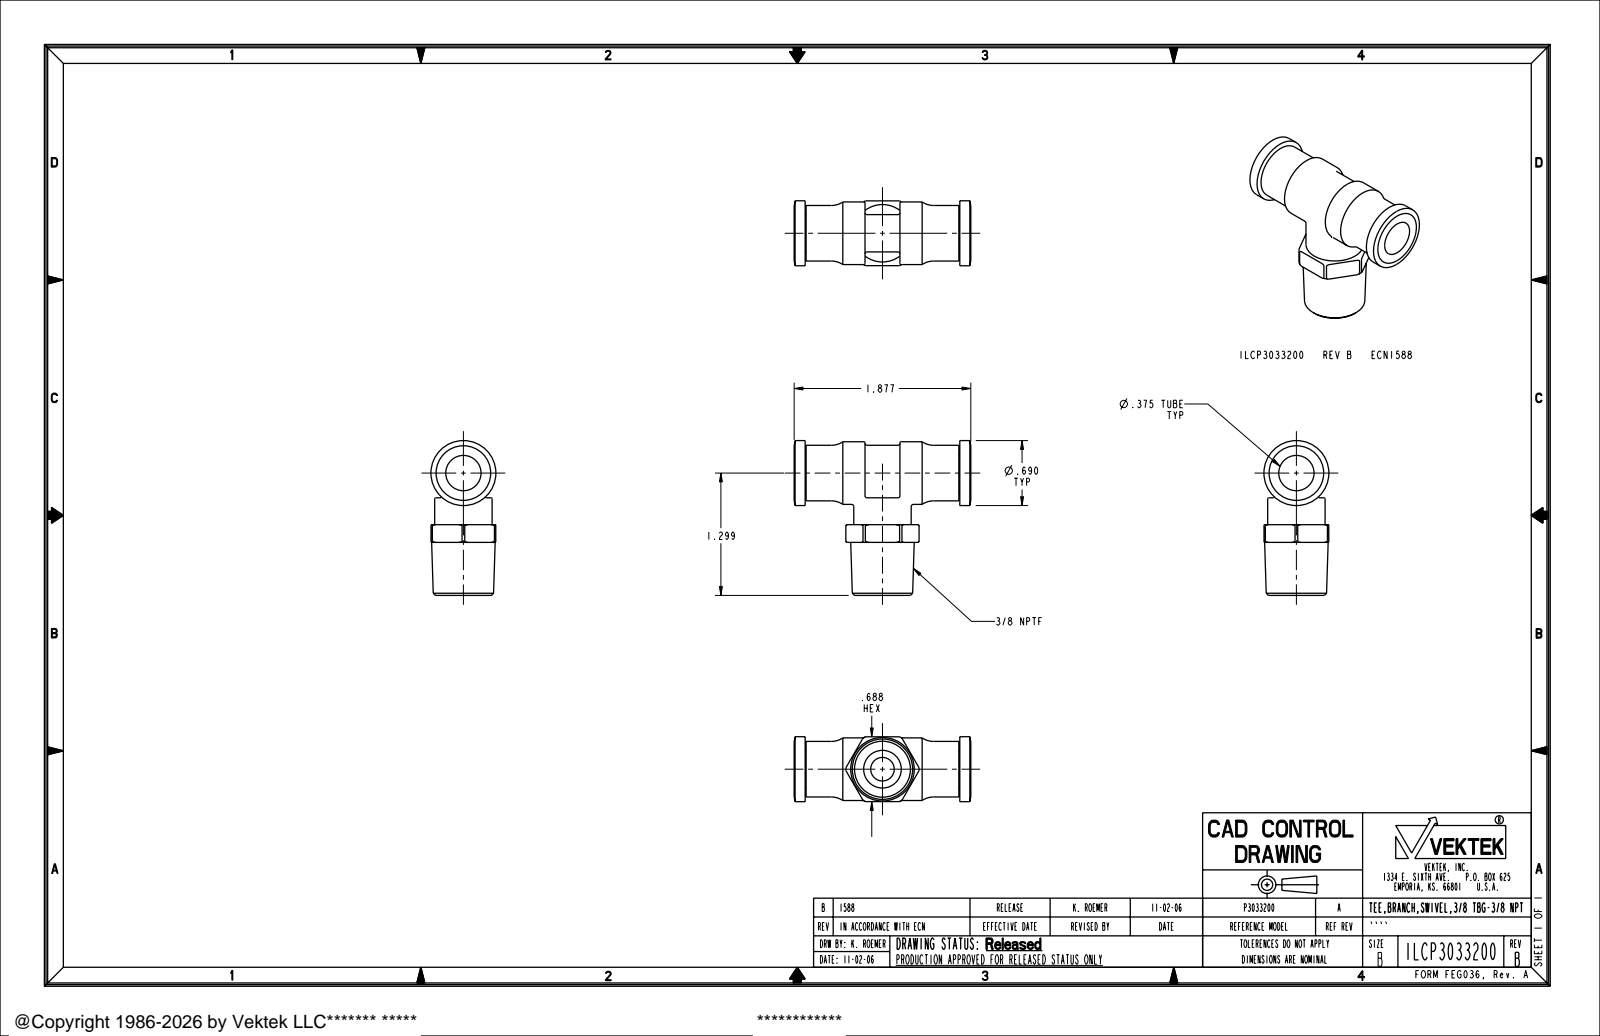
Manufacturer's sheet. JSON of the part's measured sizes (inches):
{"part_name": "ILCP3033200", "step_written_by": "PRO/ENGINEER BY PARAMETRIC TECHNOLOGY CORPORATION, 2005180 (AUTOMOTIVE_DESIGN_CC2)", "units": "inches", "bodies": {"solids": 1, "faces": 119, "planar": 22, "cylindrical": 43, "other": 54}, "overall_size": [1.877, 1.644, 0.69], "volume_in3": 0.577, "surface_area_in2": 10.92, "round_holes": [[0.25, 1], [0.375, 1], [0.4, 1]], "round_bosses_or_shafts": [[0.69, 1], [0.665, 1], [0.61, 1], [0.59, 1], [0.39, 1]], "partial_cylinders_radius": [[0.02, 10], [0.389, 1]], "face_to_face_distances": [1.633, 0.117, 0.127, 1.75, 1.76, 1.643, 0.688, 1.623, 1.877, 0.396]}
